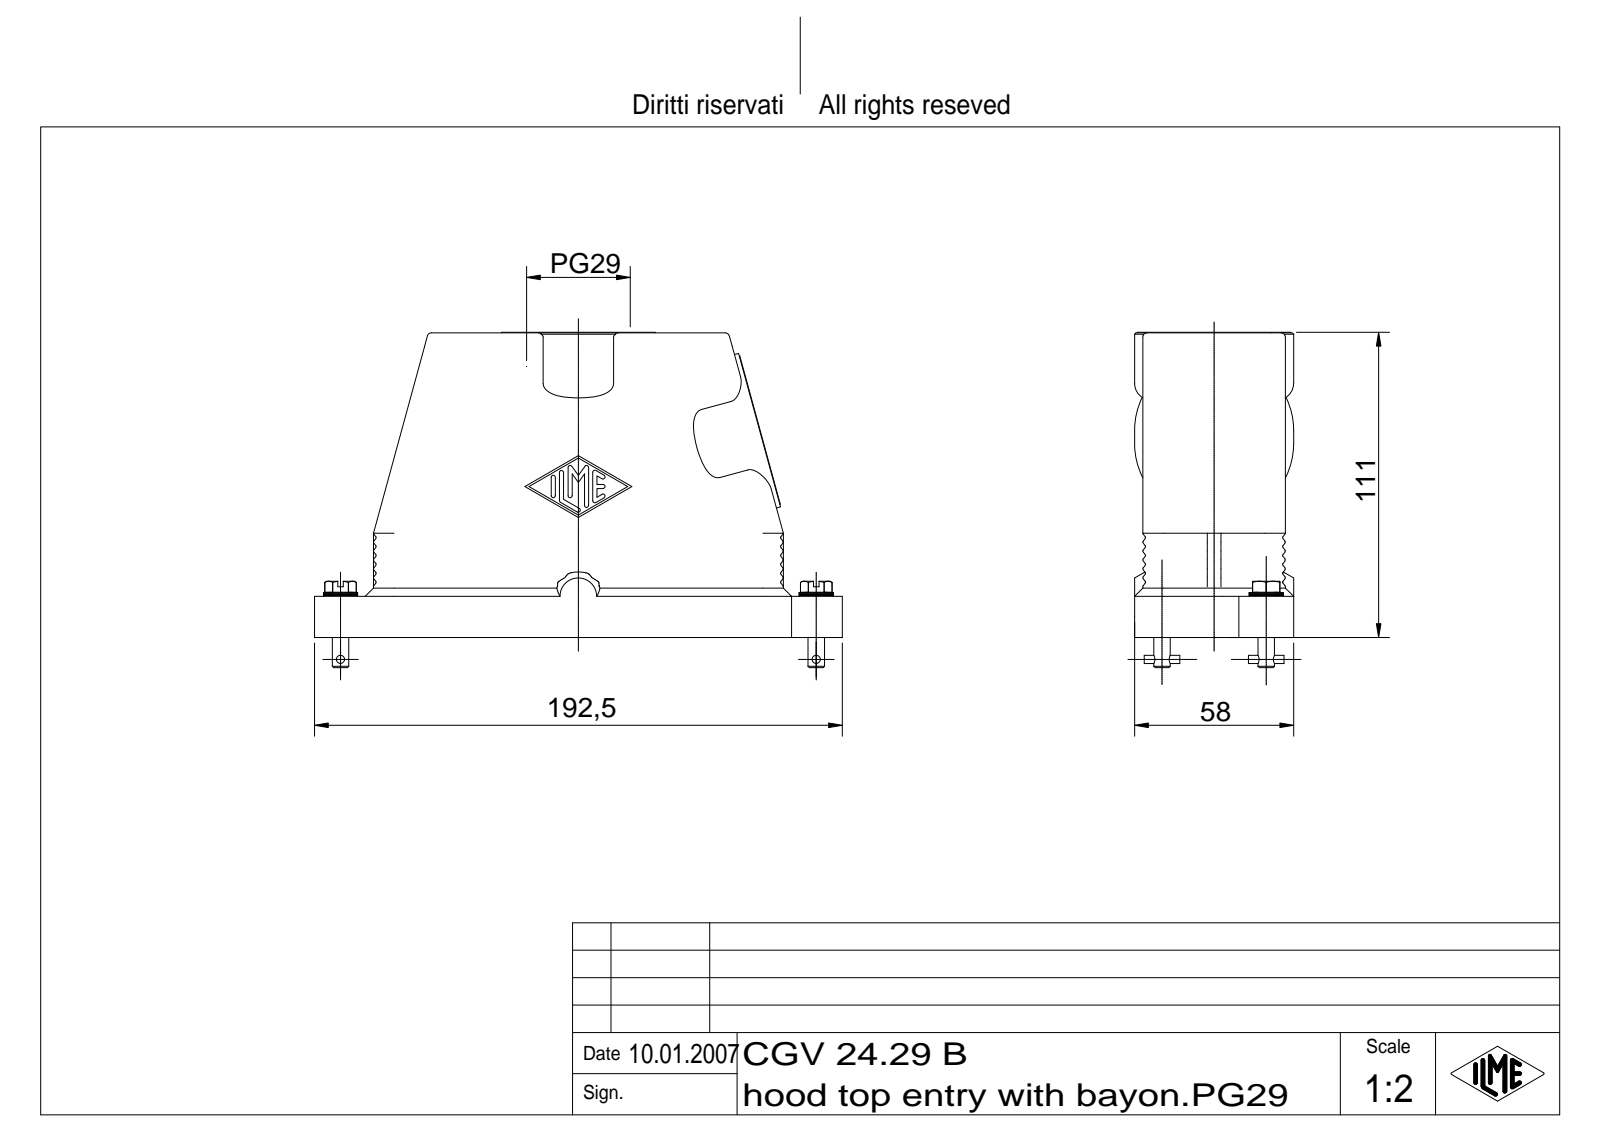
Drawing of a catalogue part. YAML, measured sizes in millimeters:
part_name: "CGV 24.29 B"
step_written_by: "Autodesk Inventor 7 (AUTOMOTIVE_DESIGN)"
units: millimeters
bodies: {solids: 3, faces: 779, planar: 193, cylindrical: 203, other: 383}
overall_size: [192.5, 122.2, 58]
volume: 251924
surface_area: 107535
round_holes:
  - {diameter: 2.46, count: 2}
  - {diameter: 3.2, count: 2}
  - {diameter: 6.6, count: 2}
  - {diameter: 15, count: 2}
  - {diameter: 35.48, count: 1}
round_bosses_or_shafts:
  - {diameter: 58, count: 2}
  - {diameter: 56, count: 2}
  - {diameter: 12.5, count: 2}
  - {diameter: 6, count: 2}
  - {diameter: 3, count: 2}
partial_cylinders:
  - {radius: 0.5, count: 39}
  - {radius: 0.75, count: 14}
  - {radius: 7.5, count: 8}
  - {radius: 6, count: 6}
  - {radius: 1.5, count: 4}
  - {radius: 3, count: 4}
  - {radius: 5.75, count: 2}
  - {radius: 10.5, count: 2}
face_to_face_distances: [3, 52, 49, 46, 6, 55, 2.5, 0.5, 58, 3.5]
hole_center_spacings: [35.18, 142.51, 107.45, 177.61]
